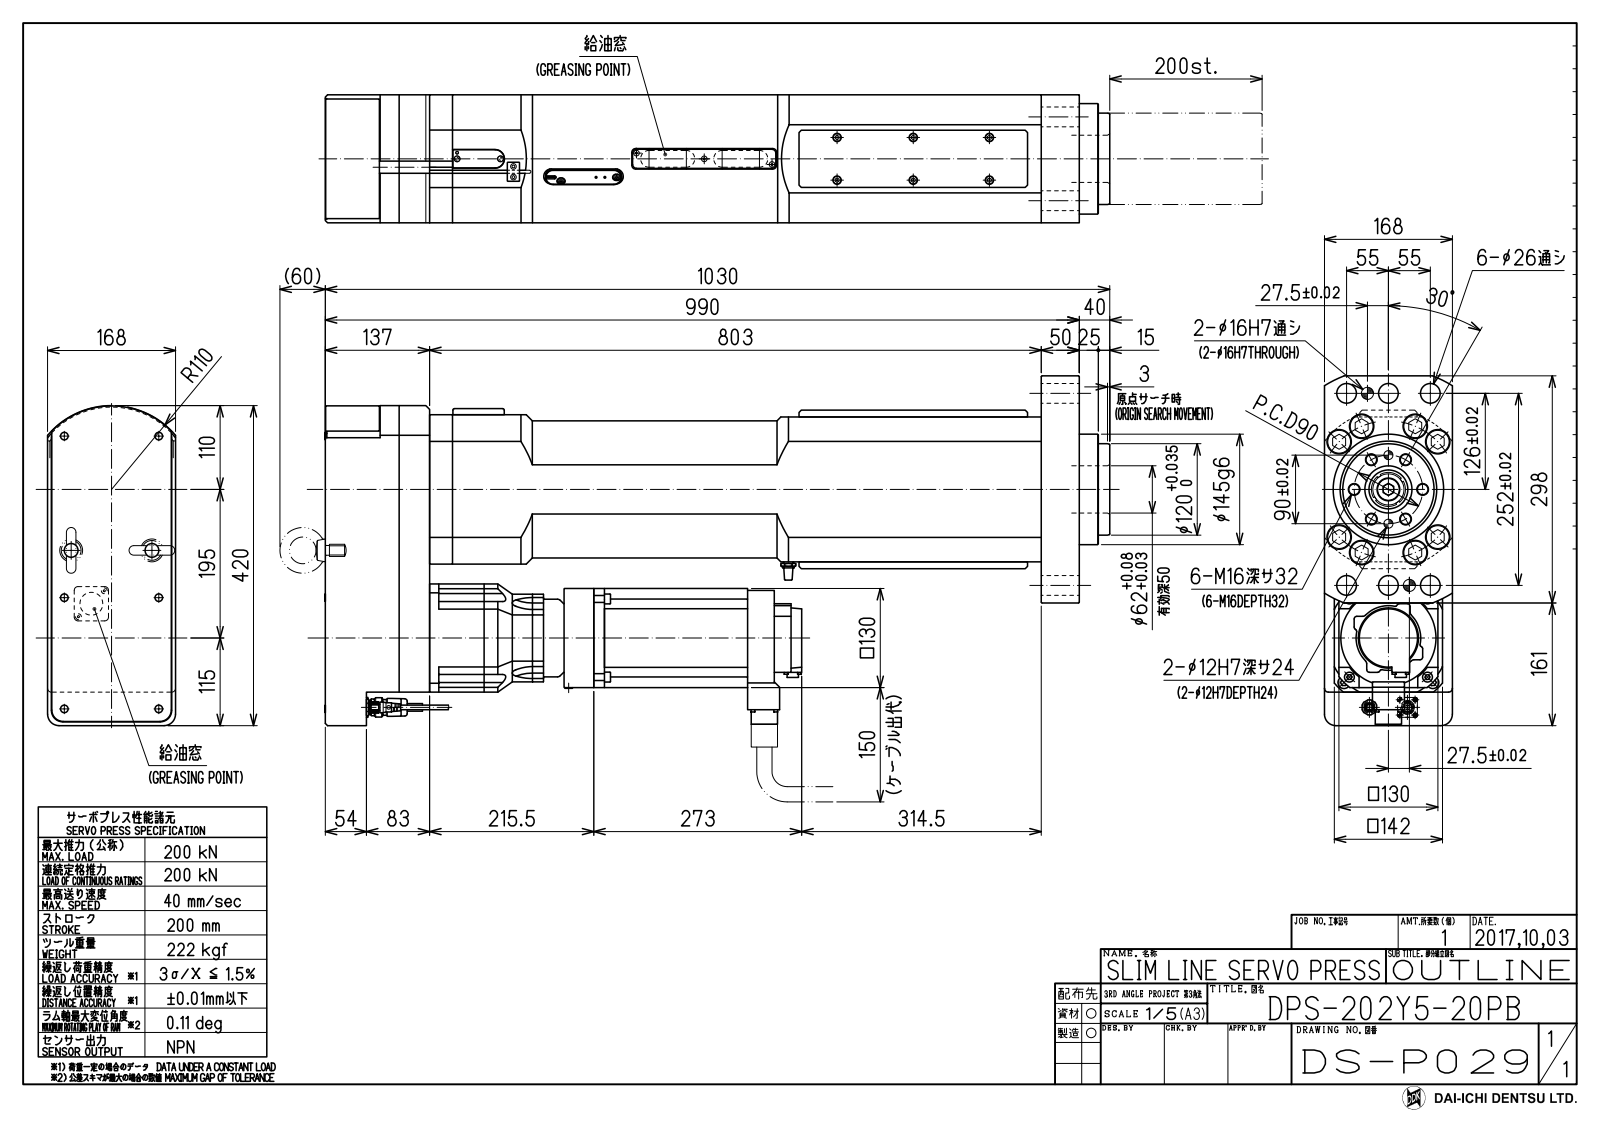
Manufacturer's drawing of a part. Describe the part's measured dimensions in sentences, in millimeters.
The part is named "DPS-202Y5-20PB(DS-P029+B)". Its 3-D file was written by "Autodesk Inventor 2021 (AUTOMOTIVE_DESIGN)". It is 1 solid with 1987 faces: 1243 planar, 421 cylindrical and 323 other. Overall it measures 1089.6 by 459 by 168 millimeters. Its volume is 40 820 000 cubic millimeters and its surface area 1 363 000 square millimeters. Round holes: 9 of diameter 11, 8 of diameter 32, 6 of diameter 13.84, 6 of diameter 26, 3 of diameter 2.46, 3 of diameter 5, 3 of diameter 14, 3 of diameter 16, 2 of diameter 8, 2 of diameter 9, 2 of diameter 12, 1 of diameter 3.24. Round bosses or shafts: 17 of diameter 10, 9 of diameter 30, 8 of diameter 5.5, 5 of diameter 16, 4 of diameter 13, 4 of diameter 11, 4 of diameter 10.5, 4 of diameter 8. Partial cylindrical surfaces (rounded edges, fillets, slot ends): 12 of radius 5, 11 of radius 10, 10 of radius 2, 8 of radius 0.4, 8 of radius 3, 6 of radius 15, 4 of radius 4.25, 4 of radius 5.75. The main face-to-face distances are 168, 6, 136, 162, 50, 19, 989.6, 149, 9, 370. The hole center spacings are 45, 90, 77.94, 257.93, 23.29, 27.5, 35.88, 45.67.
